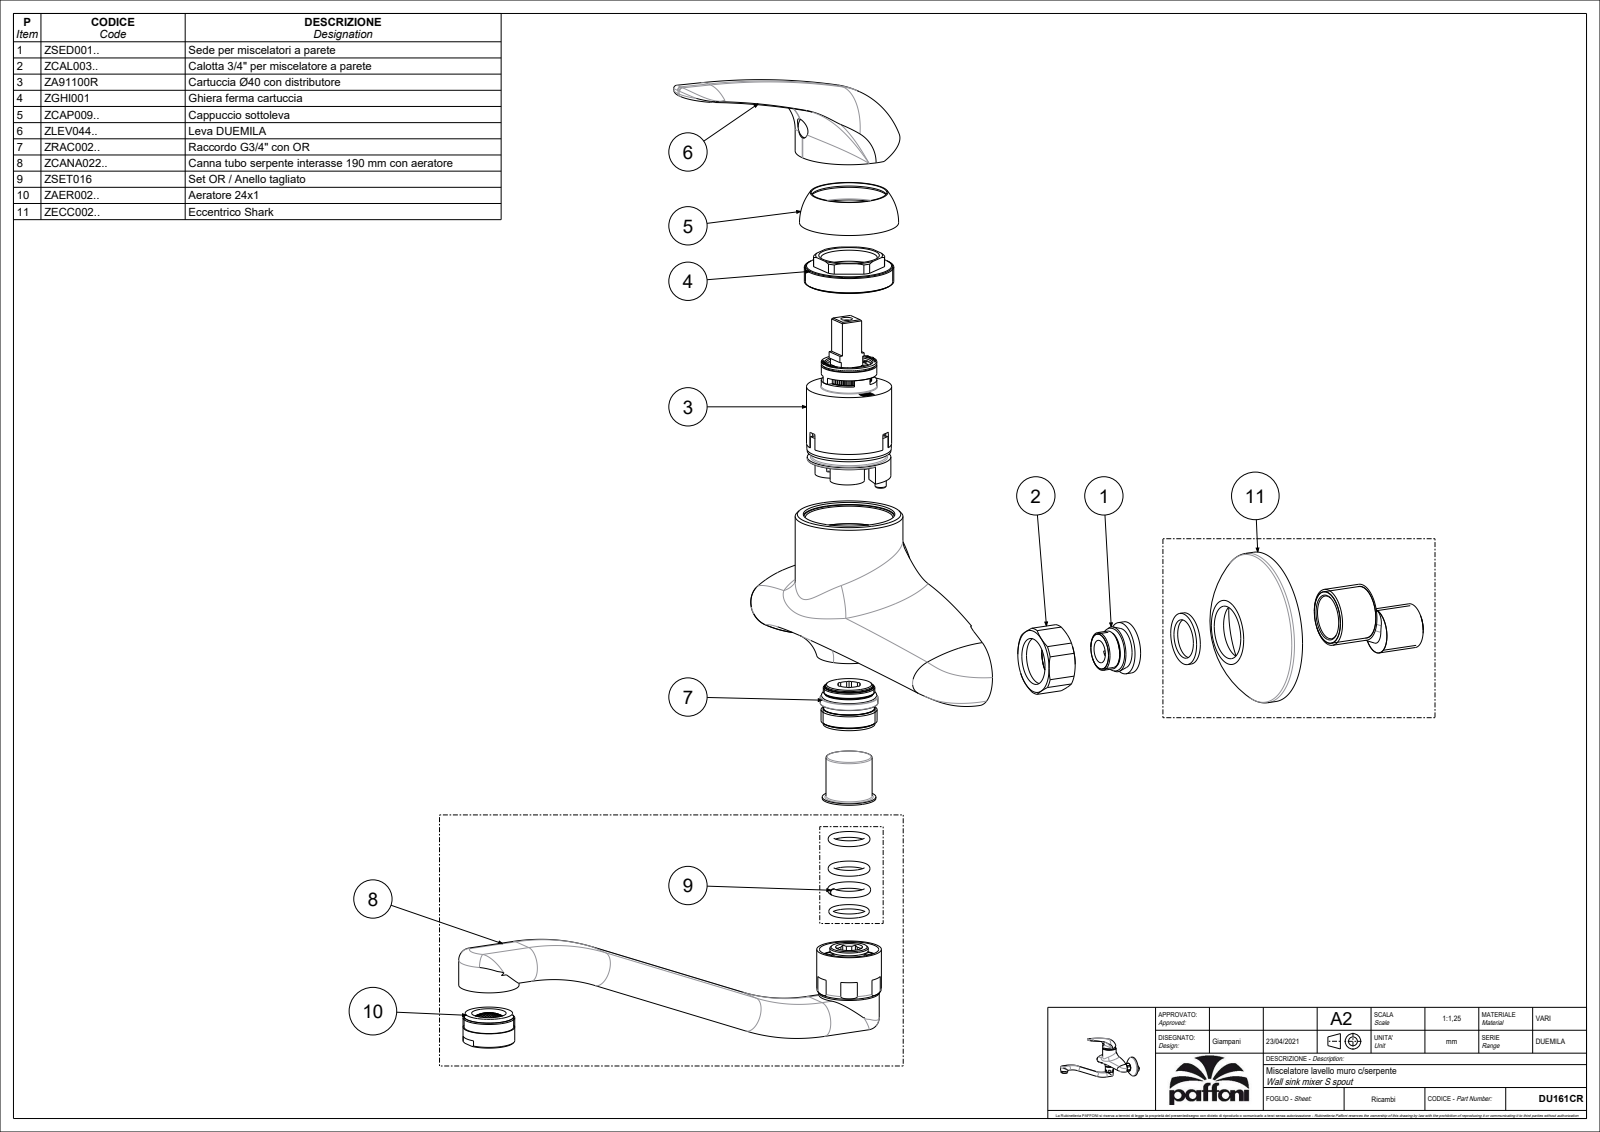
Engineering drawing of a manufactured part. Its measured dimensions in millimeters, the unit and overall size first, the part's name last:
Units: millimetres
Overall size (bounding box): 266.5 × 220 × 153.72
Round holes (diameter × count): ⌀16 ×2, ⌀9.2 ×1, ⌀17.2 ×1, ⌀18.2 ×1, ⌀18.5 ×1, ⌀20 ×1, ⌀21 ×1, ⌀21.2 ×1, ⌀23.3 ×1, ⌀27 ×1
Round bosses / shafts (diameter × count): ⌀70 ×2, ⌀28 ×2, ⌀24 ×2, ⌀50 ×1, ⌀30 ×1, ⌀26.8 ×1, ⌀26 ×1, ⌀18.1 ×1
Partial cylindrical surfaces — rounded edges, fillets, slot ends (radius × count): R7.2 ×6, R8 ×6, R1.5 ×2, R15 ×2, R15.5 ×2, R20.5 ×2, R24 ×2, R24.5 ×2
Main face-to-face distances: 34.5, 0.8, 15.2, 35.5, 1, 1.5, 14.4, 16, 0.5, 34
Hole centre spacings: 193
Volume: 504 636 mm³ · Surface area: 105 723 mm²
Bodies: 2 solids, 314 faces (85 planar, 96 cylindrical, 133 other)
Part name (STEP PRODUCT): DU161CR
STEP written by: CREO PARAMETRIC BY PTC INC, 2020044 (CONFIG_CONTROL_DESIGN)
